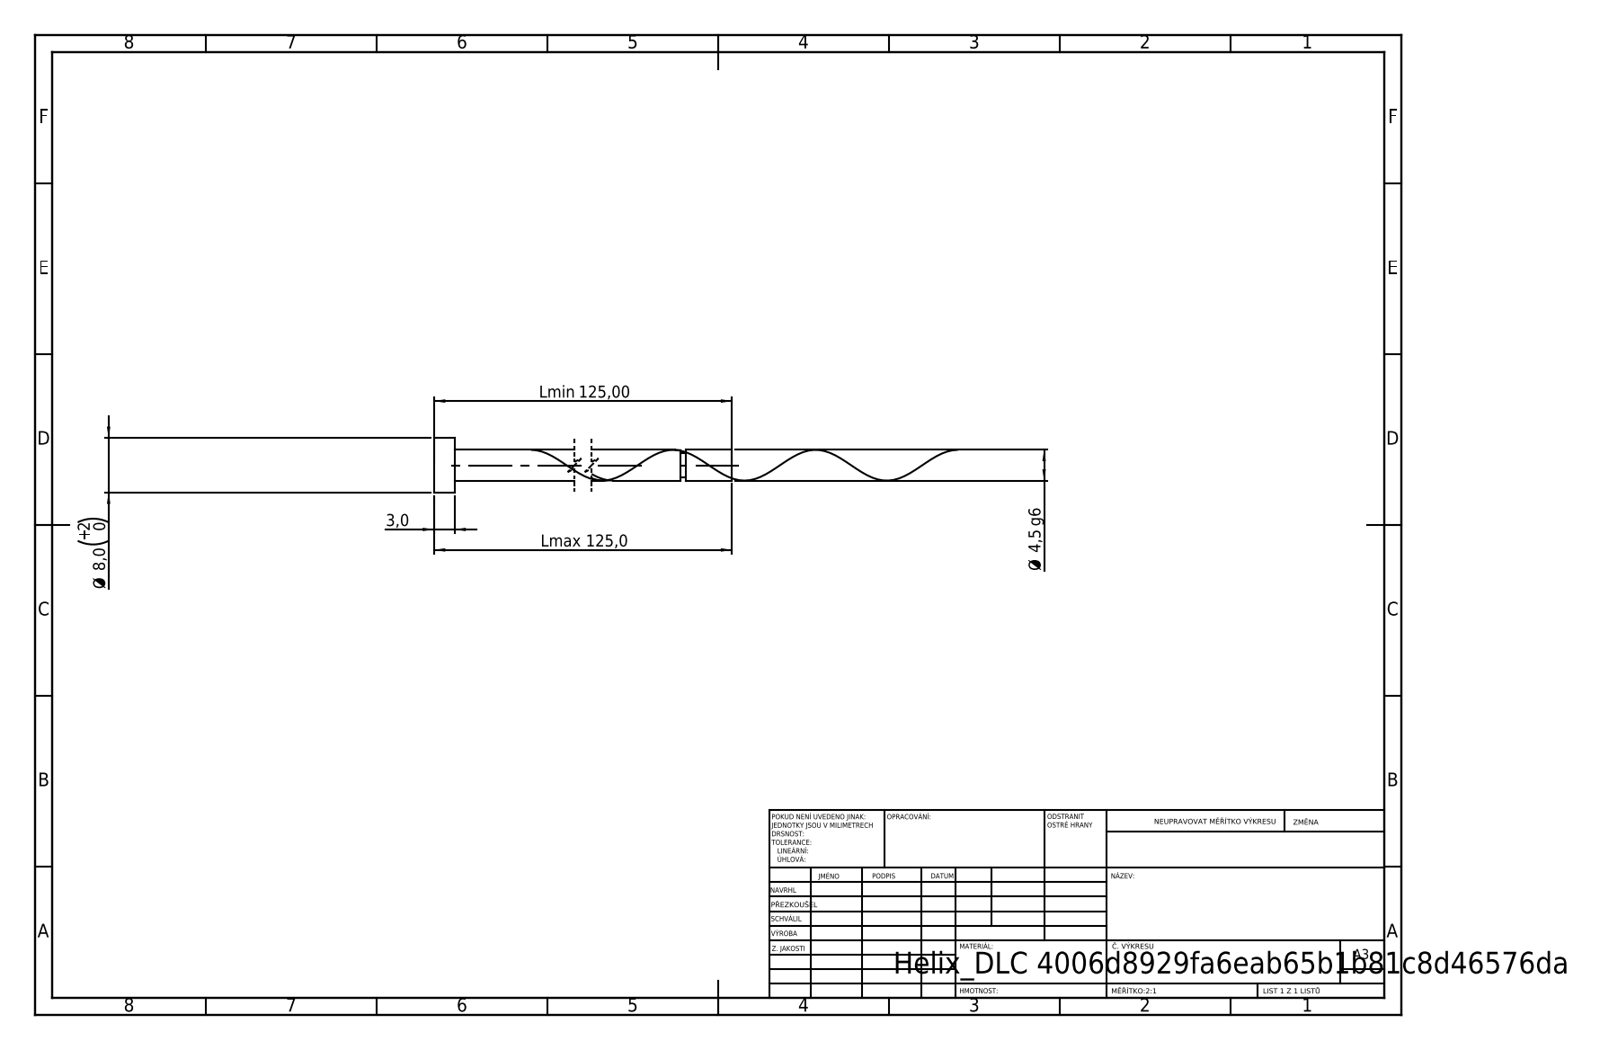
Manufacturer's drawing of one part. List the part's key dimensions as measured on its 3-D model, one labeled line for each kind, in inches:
STEP written by: SolidWorks 2019 (CONFIG_CONTROL_DESIGN)
Units: inches
Bodies: 1 solid, 21 faces (6 planar, 14 cylindrical, 1 other)
Overall size (bounding box): 4.921 × 0.315 × 0.315
Volume: 0.126 in³ · Surface area: 3.013 in²
Round bosses / shafts (diameter × count): ⌀0.315 ×1, ⌀0.177 ×1, ⌀0.142 ×1
Main face-to-face distances: 0.118, 4.921, 4.803, 4.657, 4.539, 0.265, 4.621, 4.503, 0.035, 0.3
